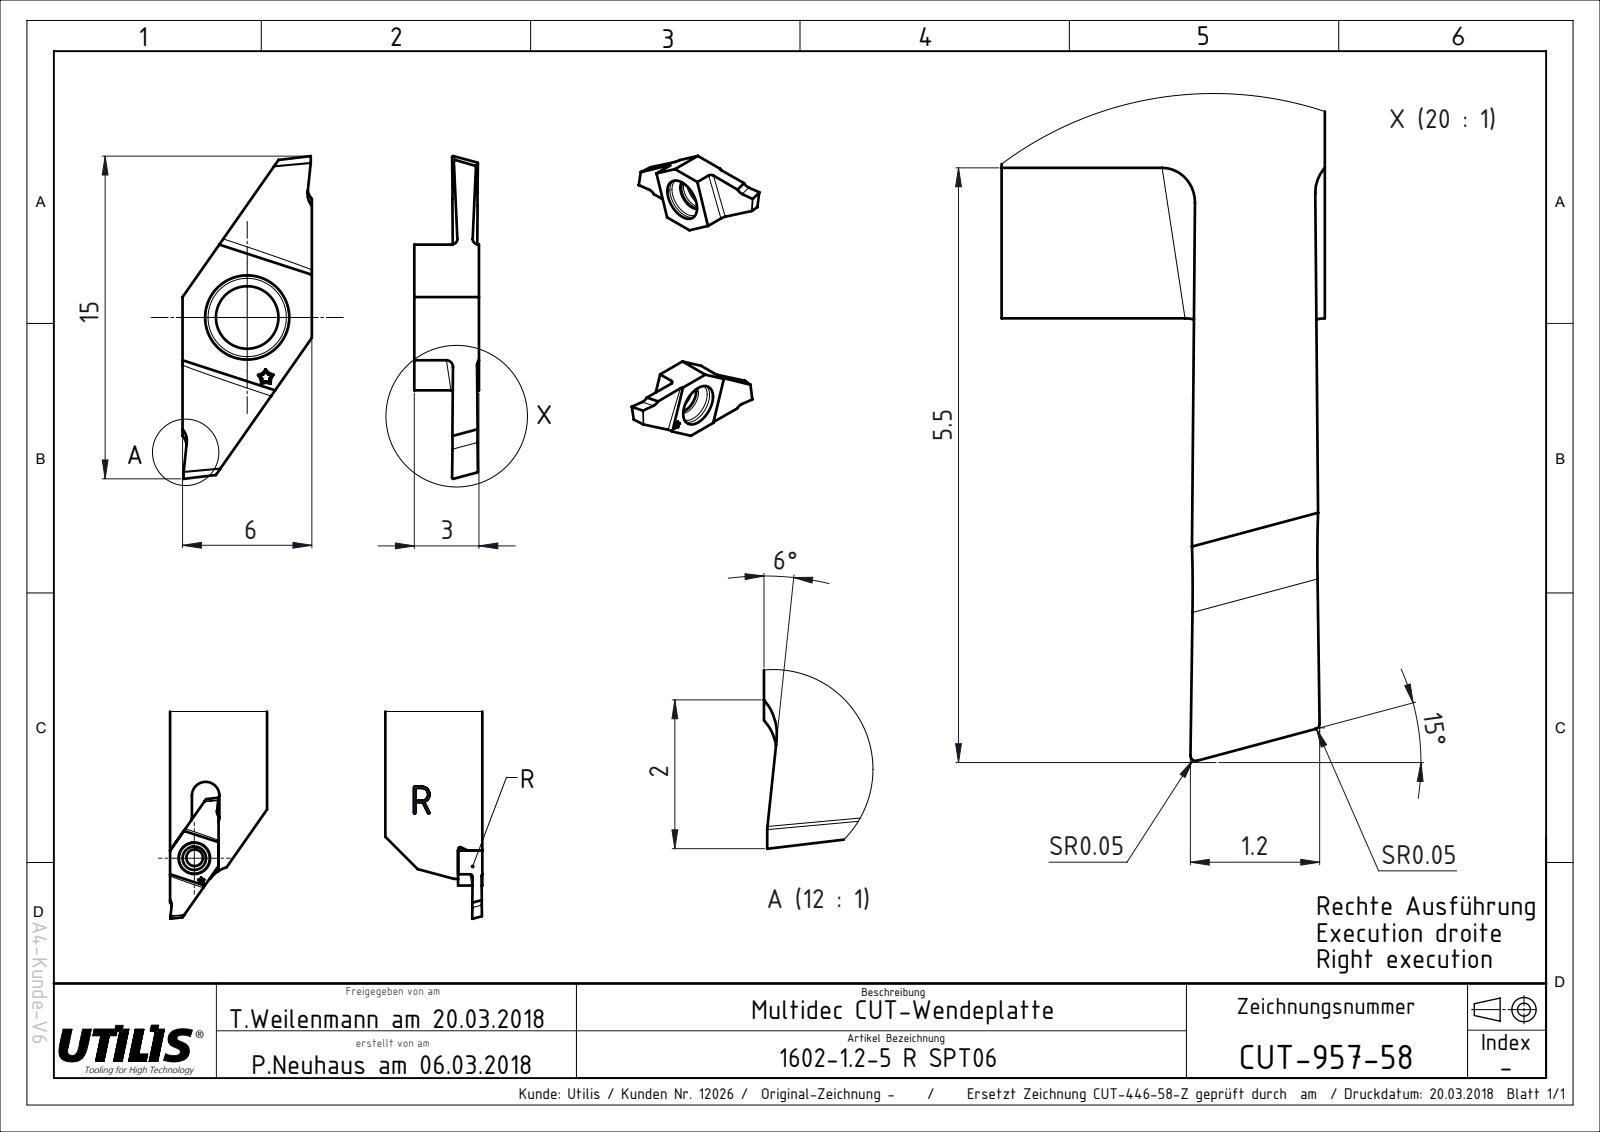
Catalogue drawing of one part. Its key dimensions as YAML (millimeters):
part_name: "CUT-957; ASME Y14.5"
step_written_by: "FormatWorks Professional (AP242_MANAGED_MODEL_BASED_3D_ENGINEERING_MIM_LF)"
units: millimeters
bodies: {solids: 1, faces: 31, planar: 25, cylindrical: 6, other: 0}
overall_size: [15, 6, 3]
volume: 105
surface_area: 211
round_holes:
  - {diameter: 2.9, count: 1}
partial_cylinders:
  - {radius: 0.3, count: 4}
face_to_face_distances: [6, 1.05, 3, 5.66, 2.93]
